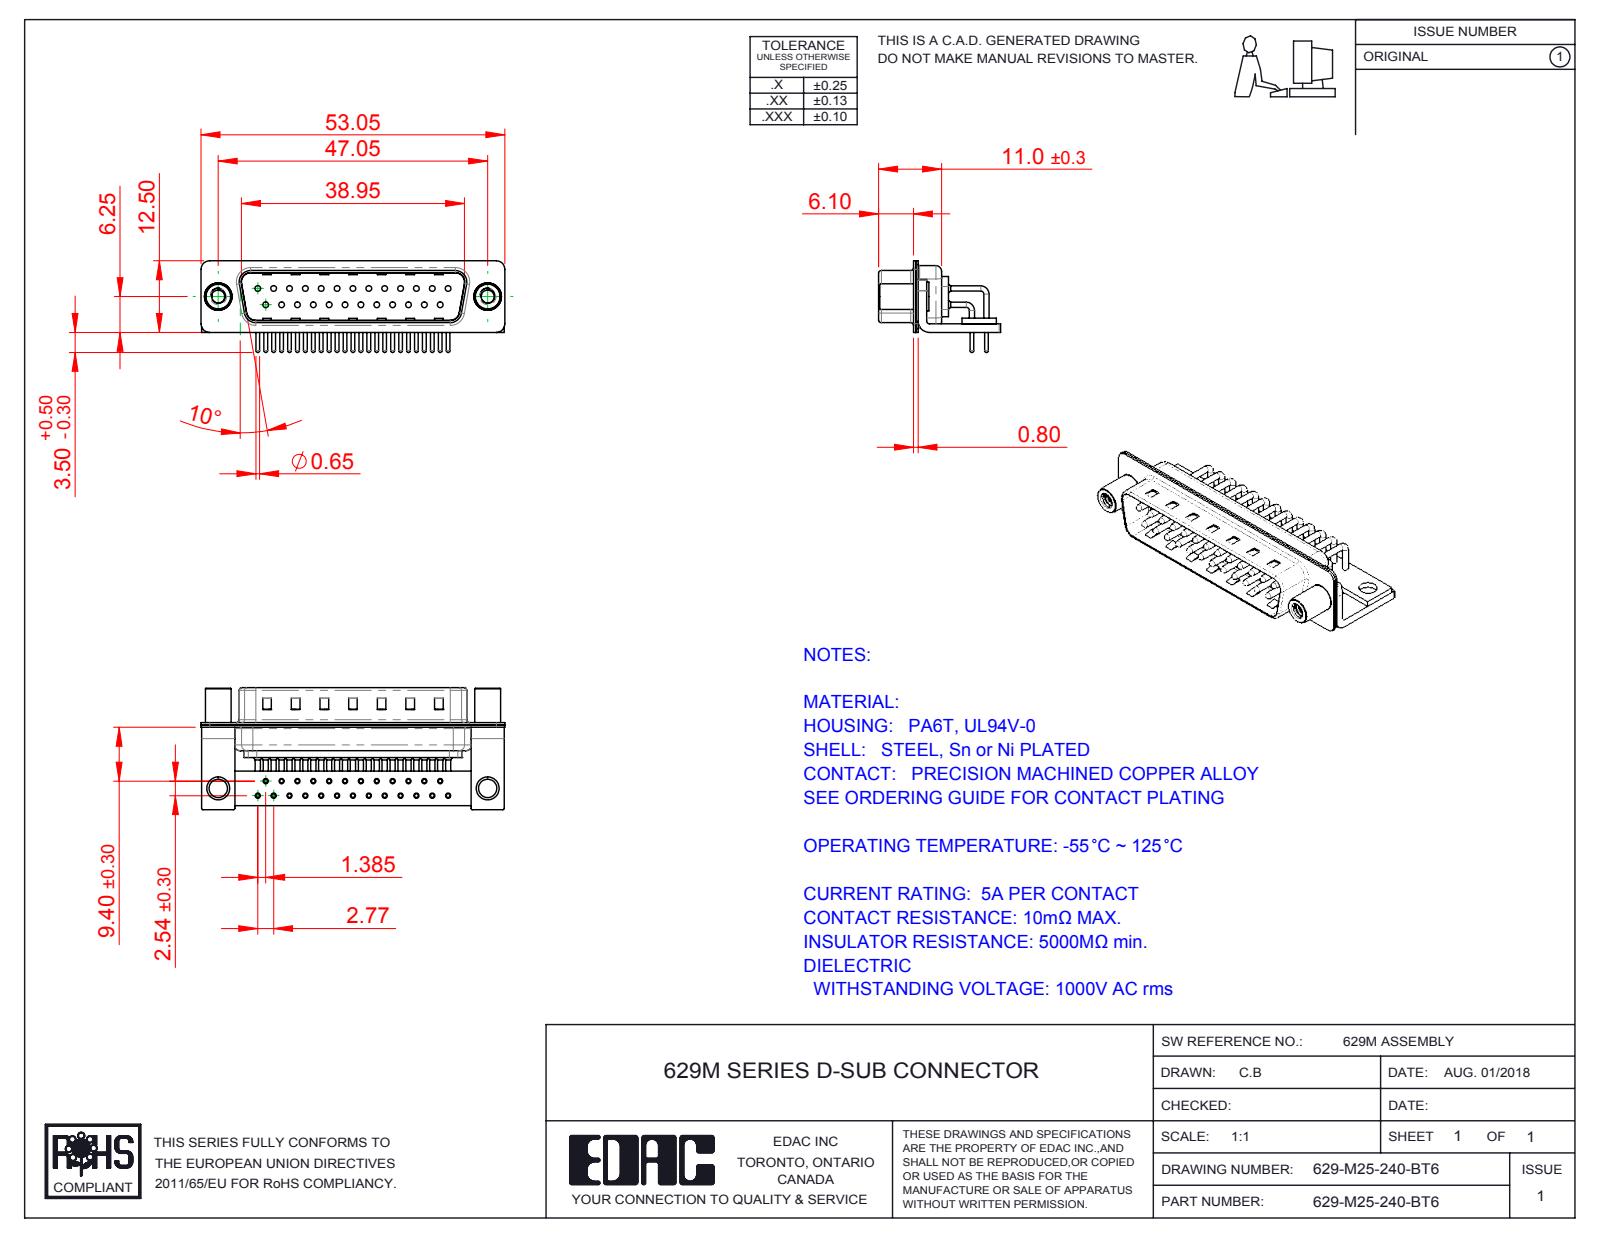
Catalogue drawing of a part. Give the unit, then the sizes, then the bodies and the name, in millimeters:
Units: millimetres
Overall size (bounding box): 53.05 × 21.3 × 16
Round holes (diameter × count): ⌀0.9 ×25, ⌀1 ×25, ⌀1.7 ×25, ⌀2 ×25, ⌀2.26 ×2, ⌀3.2 ×2, ⌀4 ×2, ⌀4.8 ×2
Round bosses / shafts (diameter × count): ⌀1.5 ×25, ⌀0.9 ×25, ⌀0.65 ×25, ⌀5 ×2, ⌀4.9 ×2, ⌀4.5 ×2
Partial cylindrical surfaces — rounded edges, fillets, slot ends (radius × count): R1.01 ×25, R0.25 ×16, R1.5 ×16, R2 ×13, R0.5 ×9, R1.6 ×8, R0.6 ×4, R0.65 ×4
Main face-to-face distances: 0.4, 0.85, 1.25, 1.5, 9.55, 0.8, 10.4, 8.3, 1, 1.9
Hole centre spacings: 2.77, 5.54, 8.31, 11.08, 13.85, 3.16, 4.87, 16.62
Volume: 3 592 mm³ · Surface area: 9 451 mm²
Bodies: 33 solids, 3276 faces (1799 planar, 1151 cylindrical, 326 other)
Part name (STEP PRODUCT): 629M Contact Row 2; 629M Stabilizer Bracket; 629M 4-40 Threaded Standoff; 629M Shell Rear_25 Contacts (+5 more)
STEP written by: SolidWorks 2016 (CONFIG_CONTROL_DESIGN)
